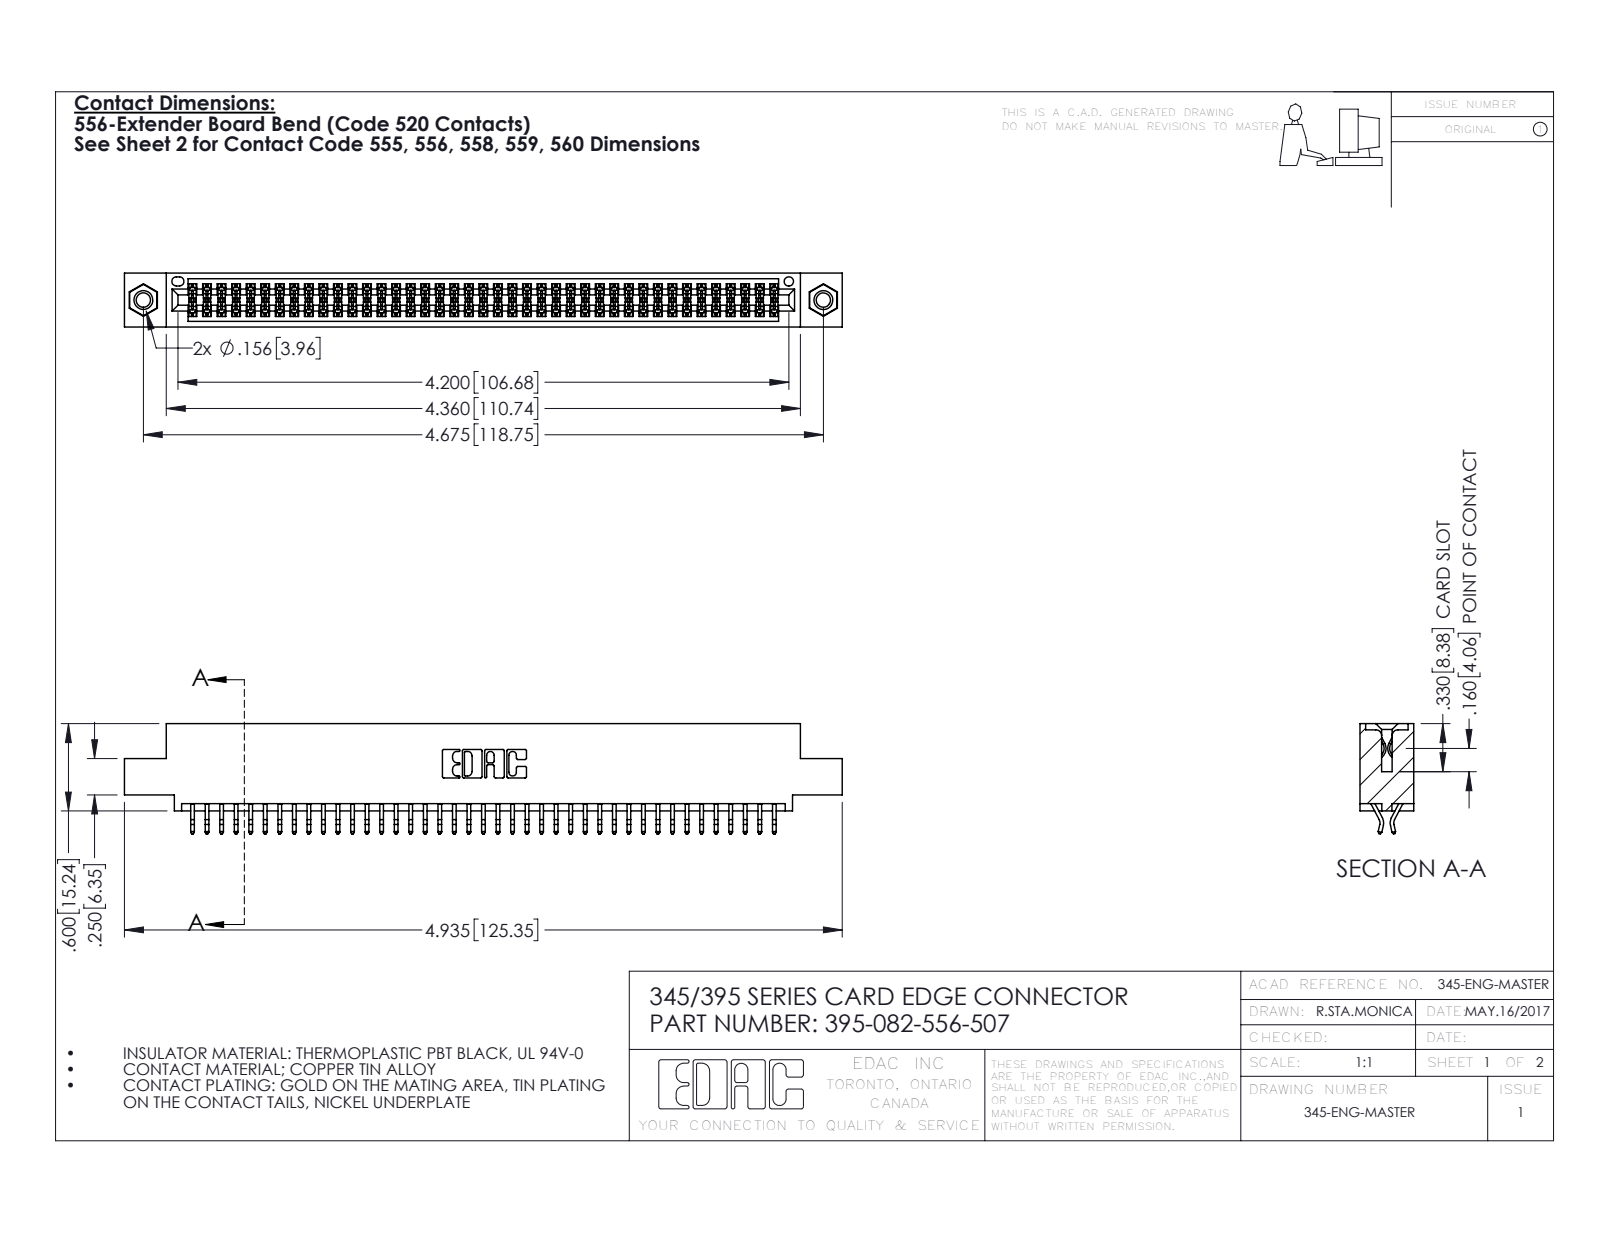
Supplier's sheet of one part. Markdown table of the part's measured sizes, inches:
| quantity | value |
| --- | --- |
| part name | 345 Part_0.110 Offset - 0.156 Dia-TI; 345-292-001_556 Tail; 345-250-001_345-250-005-103; 395-082-556-507 |
| STEP written by | SolidWorks 2016 (CONFIG_CONTROL_DESIGN) |
| units | inches |
| bodies | 85 solids, 4782 faces (3150 planar, 1616 cylindrical, 16 other) |
| overall size | 4.935 × 0.757 × 0.37 |
| volume | 0.737 in³ |
| surface area | 27.72 in² |
| round holes (diameter × count) | 0.098 × 2, 0.125 × 2, 0.156 × 2, 0.064 × 1 |
| round bosses / shafts (diameter × count) | 0.155 × 2 |
| partial cylindrical surfaces (radius × count) | 0.006 × 123, 0.01 × 22, 0.007 × 6, 0.031 × 6, 0.026 × 3, 0.01 × 2, 0.014 × 2, 0.019 × 2 |
| main face-to-face distances | 0.072, 0.298, 0.37, 0.2, 0.025, 0.098, 0.272, 0.225, 0.175, 0.149 |
| hole center spacings | 0.27, 4.439, 4.675 |
